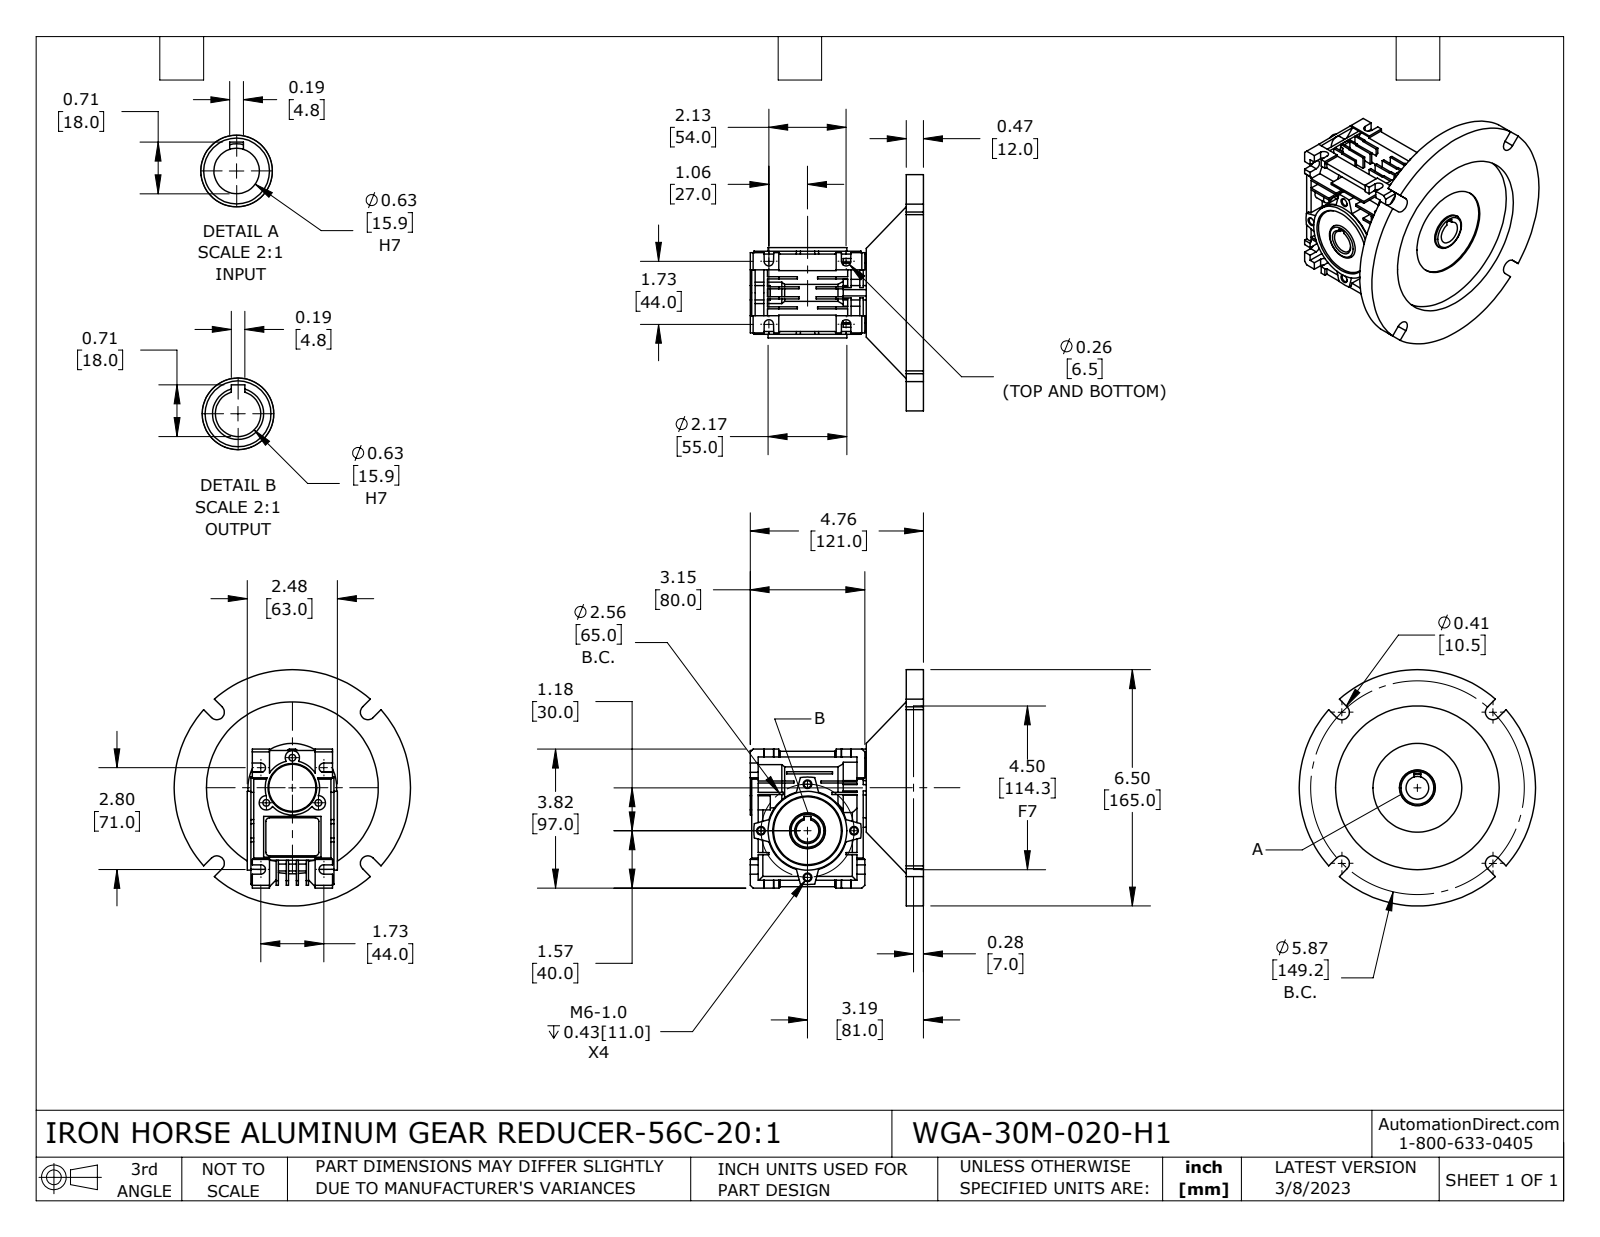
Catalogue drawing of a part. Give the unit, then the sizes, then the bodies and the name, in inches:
Units: inches
Overall size (bounding box): 6.496 × 6.496 × 4.764
Round holes (diameter × count): ⌀0.194 ×4, ⌀0.194 ×4, ⌀0.183 ×3, ⌀0.625 ×2, ⌀2.441 ×1, ⌀4.5 ×1
Round bosses / shafts (diameter × count): ⌀6.496 ×1, ⌀2.205 ×1, ⌀2.165 ×1, ⌀1.496 ×1, ⌀0.984 ×1
Partial cylindrical surfaces — rounded edges, fillets, slot ends (radius × count): R0.128 ×8, R0.197 ×7, R0.098 ×4, R0.207 ×4, R0.374 ×1, R0.669 ×1, R0.846 ×1, R1.476 ×1
Main face-to-face distances: 0.276, 0.059, 0.039, 0.472, 0.217, 0.197, 0.177, 0.551, 0.335, 0.157
Hole centre spacings: 1.28, 1.809, 0.827, 1.432, 2.559, 1.432
Volume: 39.8 in³ · Surface area: 198.1 in²
Bodies: 1 solid, 682 faces (442 planar, 168 cylindrical, 72 other)
Part name (STEP PRODUCT): WGA-30M-020-H1
STEP written by: SolidWorks 2021 (CONFIG_CONTROL_DESIGN)
